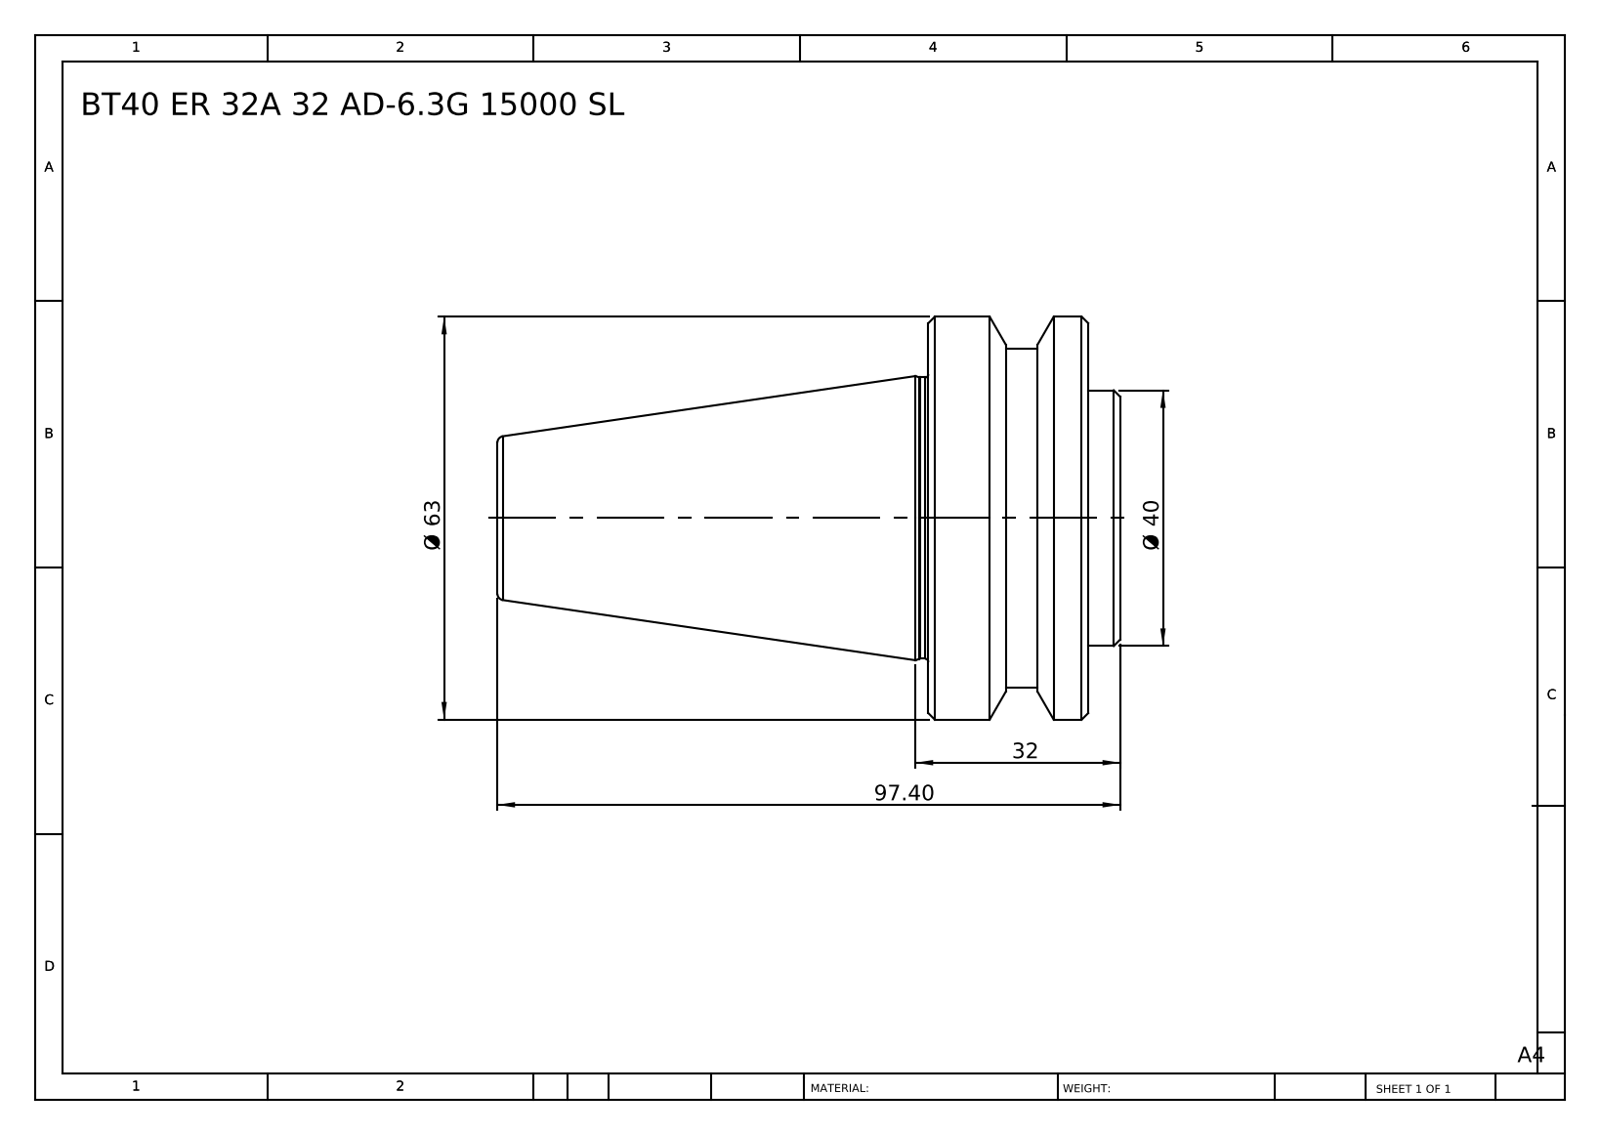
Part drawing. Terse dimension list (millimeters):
name: BT40 ER 32A 32 AD-6.3G 15000 SL
written by: SolidWorks 2014 (CONFIG_CONTROL_DESIGN)
unit: mm
bodies: 1 solid, 36 faces (6 planar, 10 cylindrical, 20 other)
size: 97.4 × 63 × 63
volume: 144 562 mm³; area: 18 885 mm²
bosses: 1× ⌀63, 1× ⌀53, 1× ⌀44, 1× ⌀40
face distances: 25, 5, 30, 97.4, 92.4, 67.4, 12.9, 17.9, 12.1, 79.5
